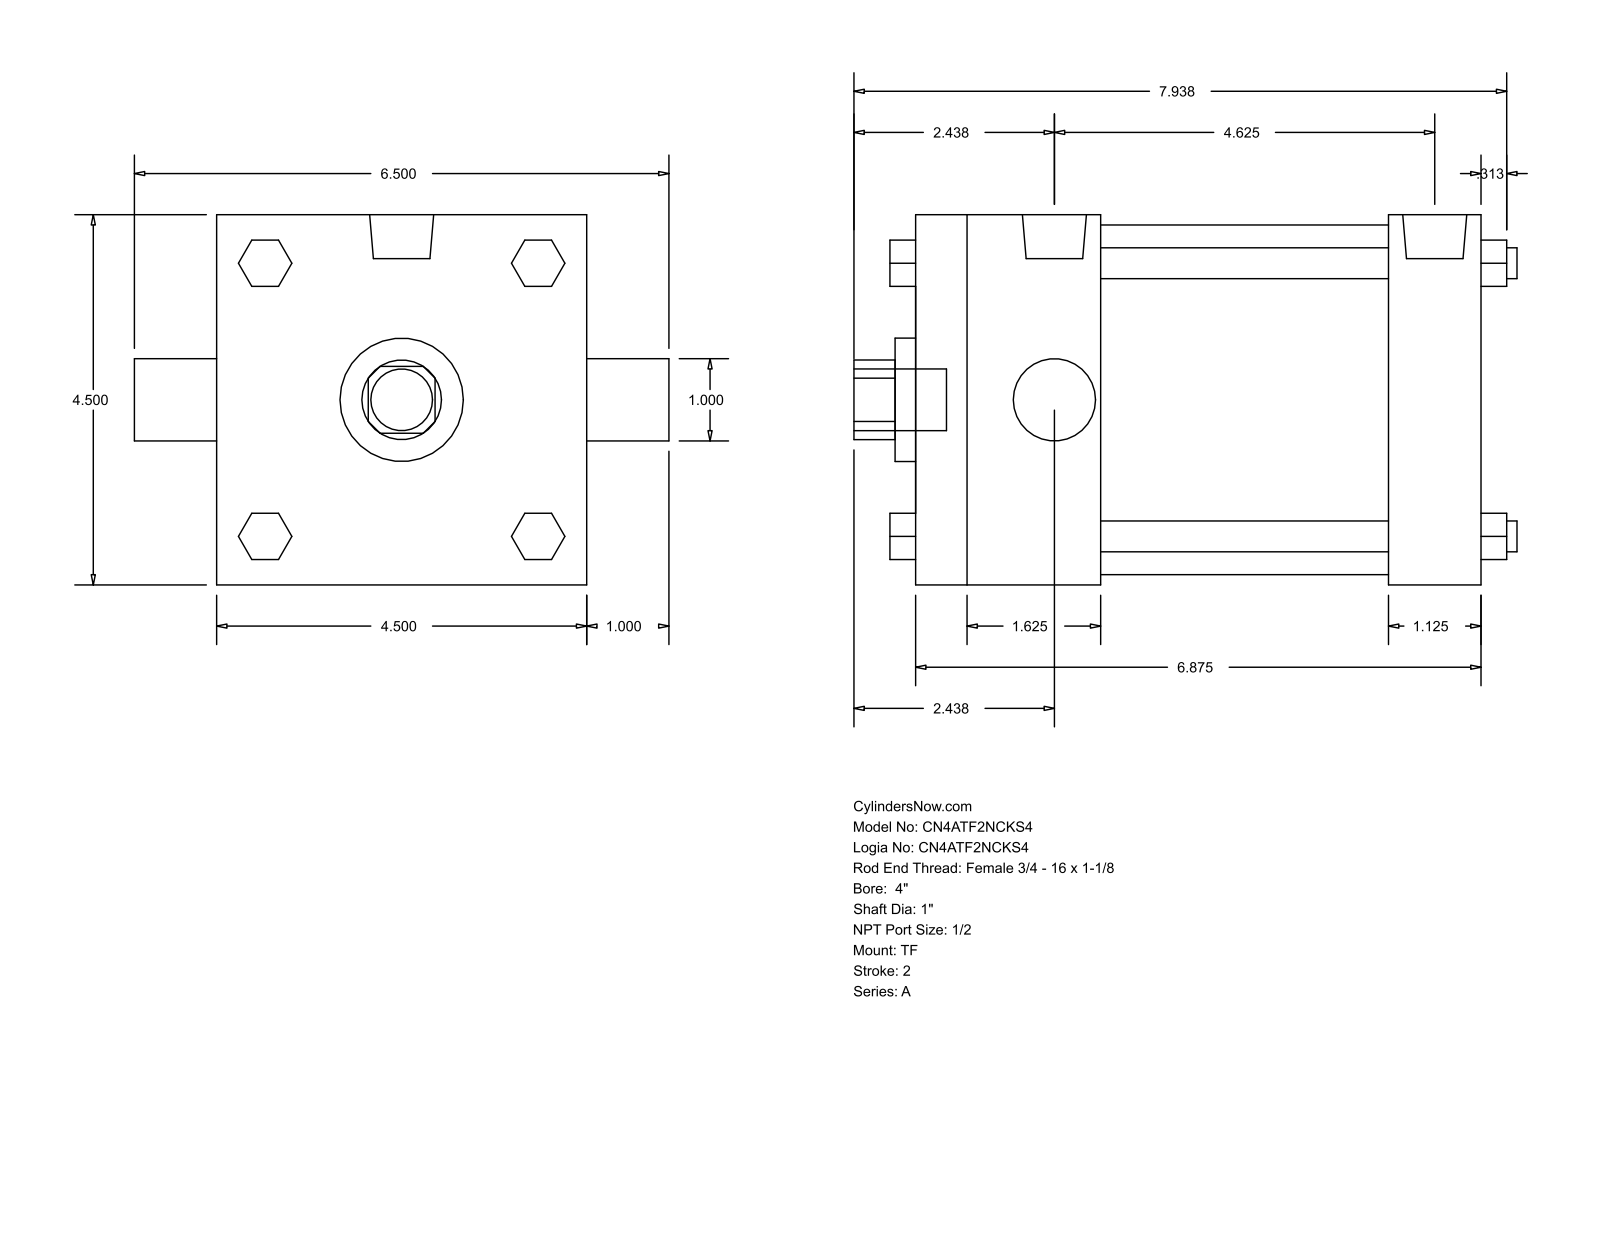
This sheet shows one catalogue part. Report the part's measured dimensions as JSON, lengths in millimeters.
{"part_name": "A_TF__0400_1", "step_written_by": "GSSL Pune (CONFIG_CONTROL_DESIGN)", "units": "millimeters", "bodies": {"solids": 0, "faces": 120, "planar": 92, "cylindrical": 28, "other": 0}, "overall_size": [204.79, 165.1, 114.3], "round_holes": [[25.4, 2], [38.1, 1], [107.95, 1]], "round_bosses_or_shafts": [[9.53, 4], [8.73, 3], [19.77, 2], [19.05, 1]], "partial_cylinders_radius": [[12.29, 1]], "face_to_face_distances": [114.3, 174.63, 146.05, 28.58, 57.15, 88.9, 117.48, 14.29, 42.16, 73.03]}
